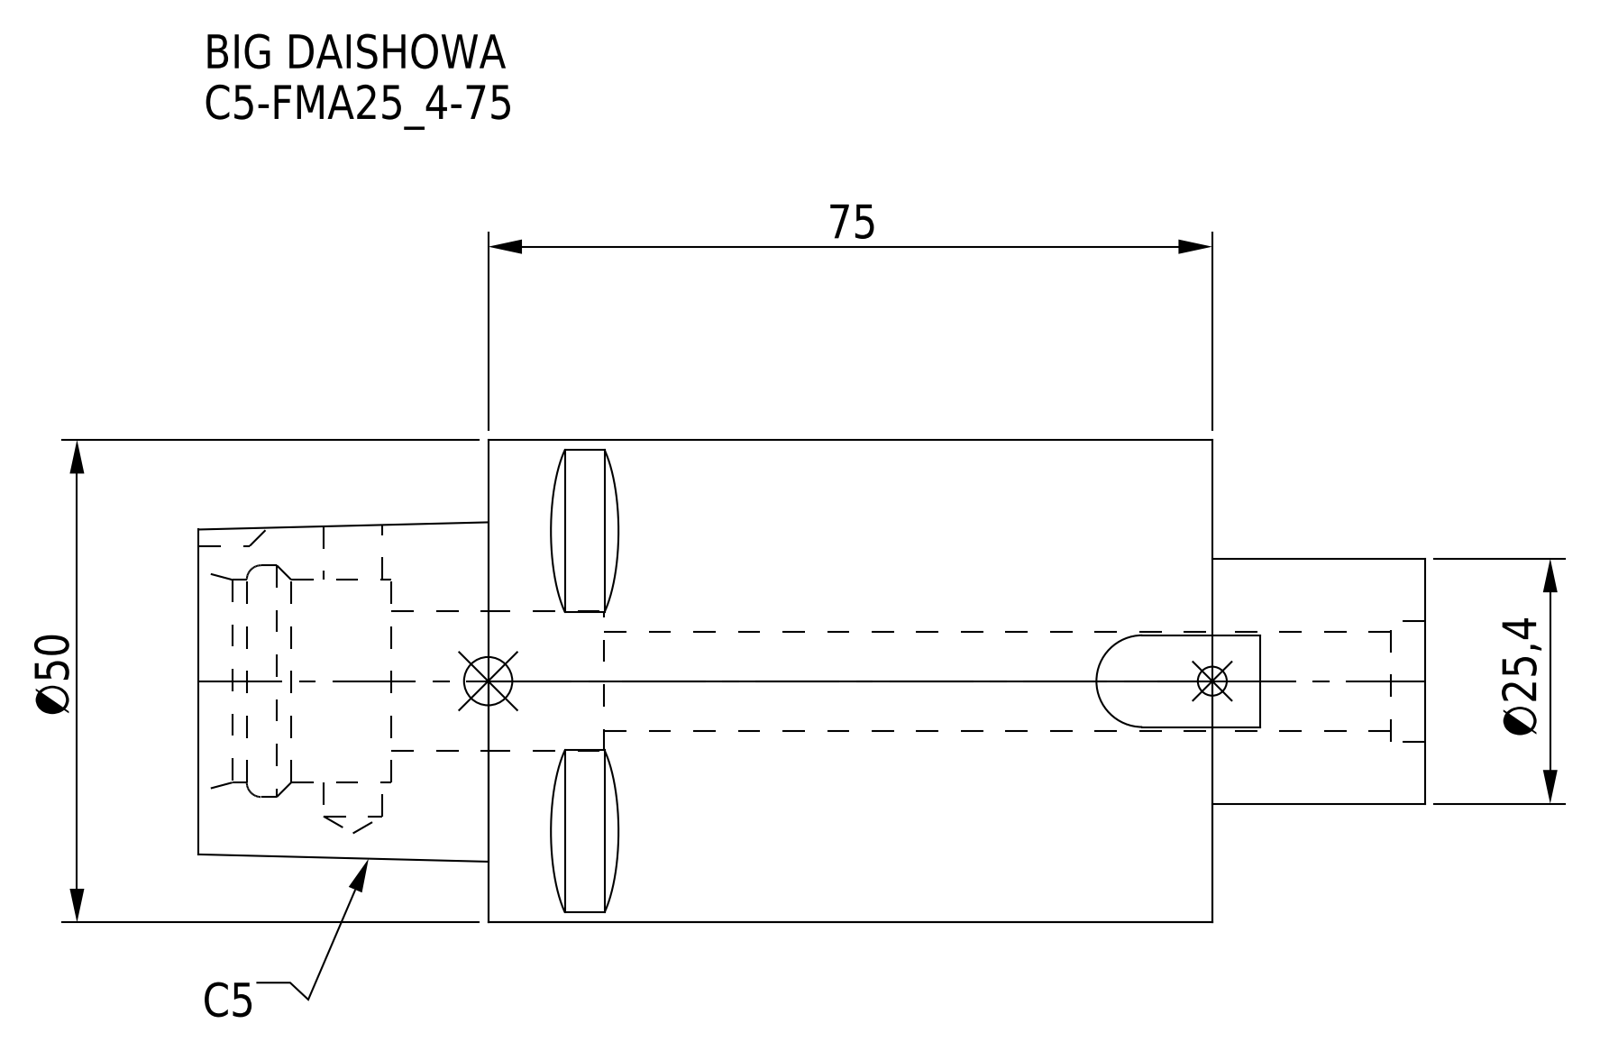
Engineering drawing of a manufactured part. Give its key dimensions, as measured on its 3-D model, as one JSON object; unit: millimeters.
{"part_name": "C5-FMA25_4-75", "step_written_by": "CREO PARAMETRIC BY PTC INC, 2016380 (AUTOMOTIVE_DESIGN)", "units": "millimeters", "bodies": {"solids": 1, "faces": 70, "planar": 39, "cylindrical": 21, "other": 10}, "overall_size": [127, 50, 50], "volume_mm3": 167520, "surface_area_mm2": 26377, "round_holes": [[6.1, 1], [10.25, 1], [12.5, 1], [14.5, 1], [21, 1], [24, 1]], "round_bosses_or_shafts": [[50, 1], [25.4, 1]], "partial_cylinders_radius": [[4, 1]], "face_to_face_distances": [75, 22, 97, 127, 105, 30, 85, 17, 5, 80]}
